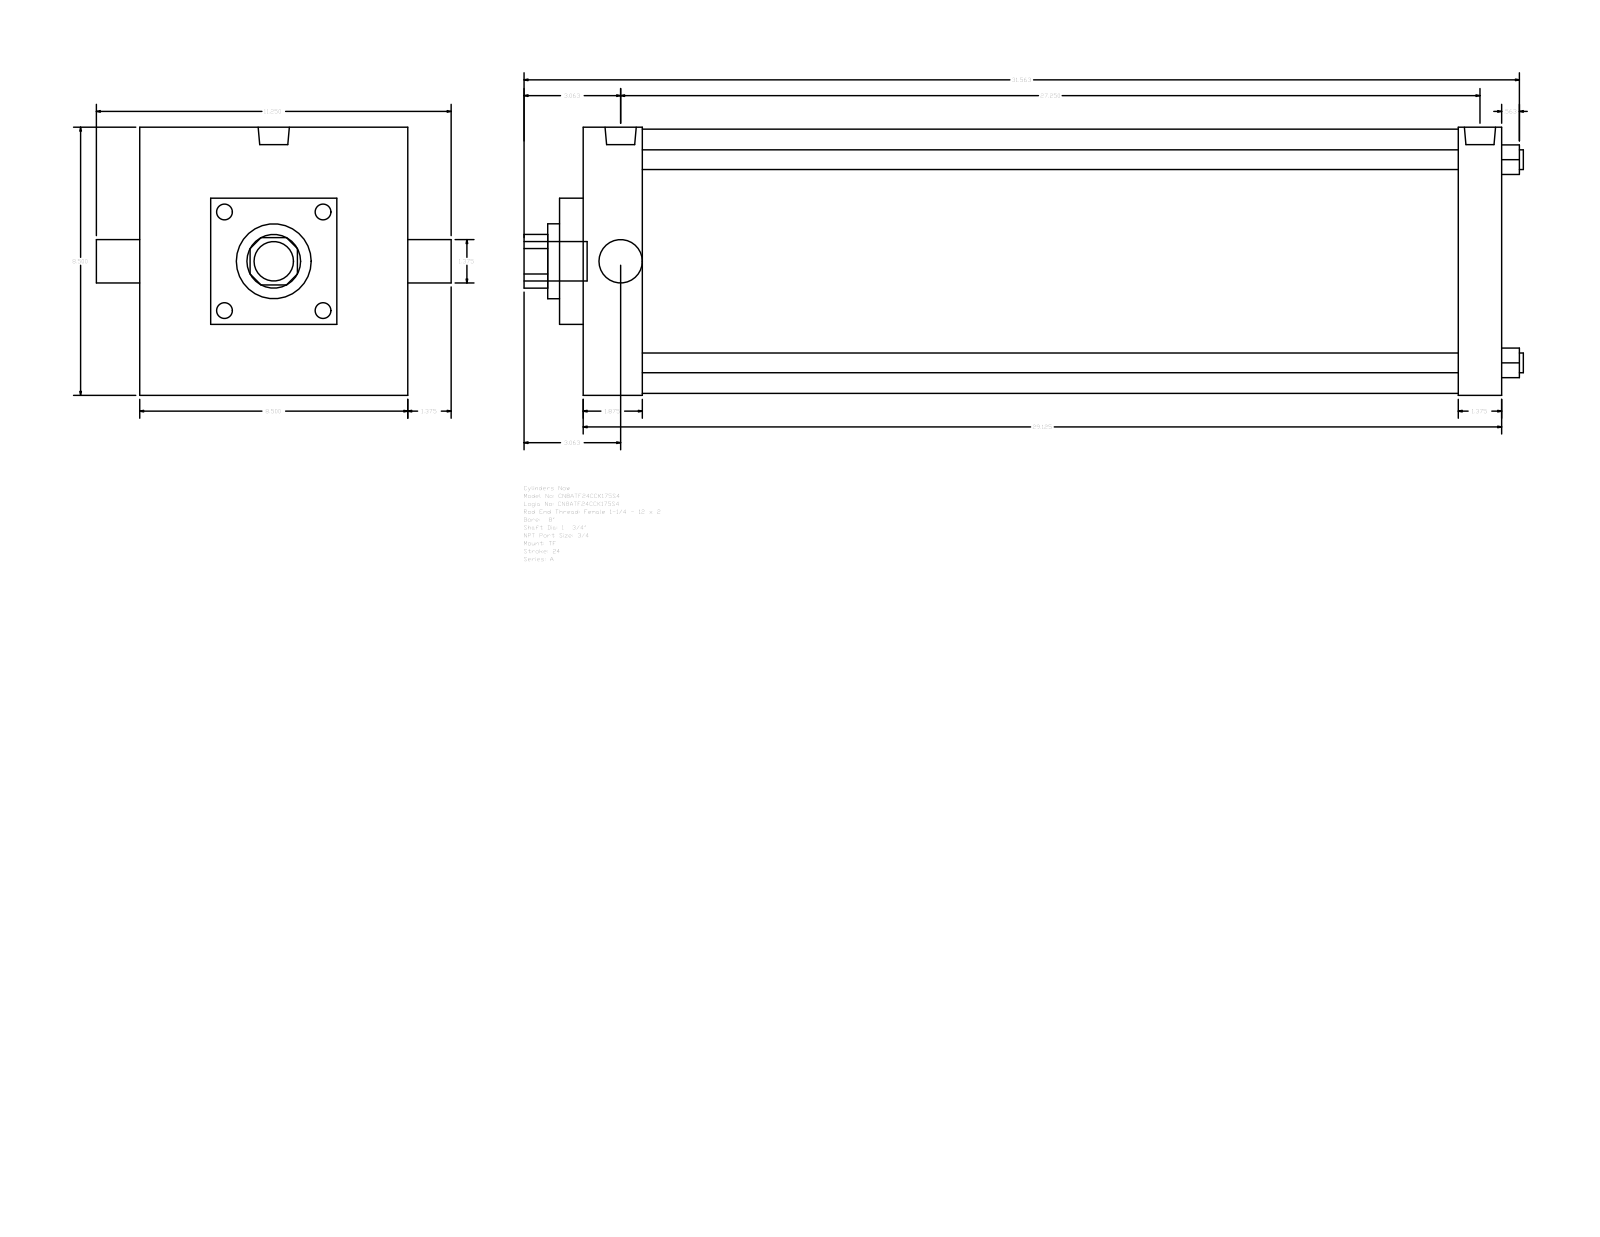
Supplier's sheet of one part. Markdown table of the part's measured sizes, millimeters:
| quantity | value |
| --- | --- |
| part name | A_TF__0800_1.75 |
| STEP written by | GSSL Pune (CONFIG_CONTROL_DESIGN) |
| units | millimeters |
| bodies | 0 solids, 89 faces (65 planar, 24 cylindrical, 0 other) |
| overall size | 804.86 × 285.75 × 215.9 |
| round holes (diameter × count) | 15.88 × 4, 34.92 × 1, 44.45 × 1, 60.33 × 1, 212.72 × 1 |
| round bosses / shafts (diameter × count) | 15.08 × 3, 25.12 × 2, 31.75 × 1 |
| partial cylindrical surfaces (radius × count) | 21.63 × 1 |
| main face-to-face distances | 739.78, 215.9, 34.92, 47.63, 692.15, 704.86, 657.23, 19.05, 57.15, 158.75 |
| hole center spacings | 115.67, 163.58, 231.34 |
